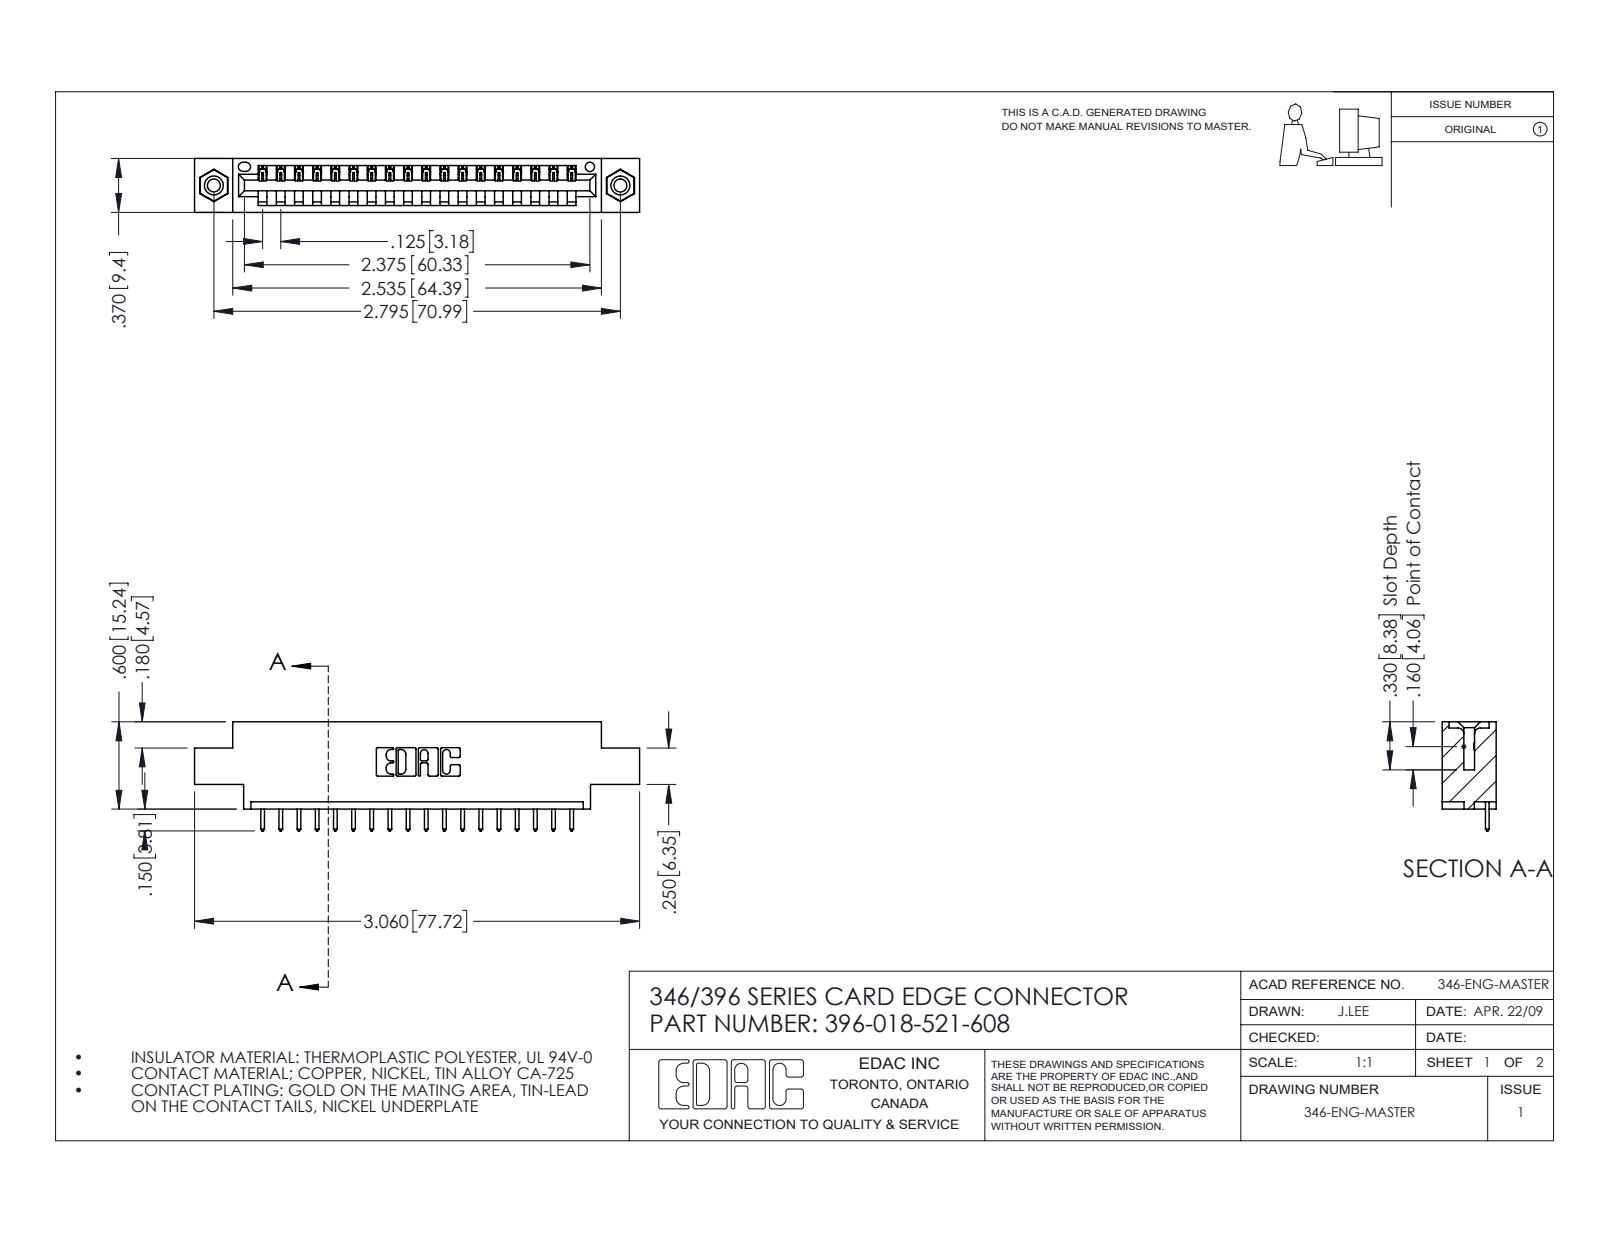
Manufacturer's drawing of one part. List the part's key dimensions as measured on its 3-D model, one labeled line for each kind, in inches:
Part name (STEP PRODUCT): 346 Part_0.170 Offset - 0.156 Dia-TI; 345-292-001_345-293-121; 345-250-001_345-250-003-102; 396-018-521-608
STEP written by: SolidWorks 2016 (CONFIG_CONTROL_DESIGN)
Units: inches
Bodies: 21 solids, 1230 faces (832 planar, 382 cylindrical, 16 other)
Overall size (bounding box): 3.06 × 0.75 × 0.37
Volume: 0.431 in³ · Surface area: 13.25 in²
Round holes (diameter × count): ⌀0.089 ×2, ⌀0.125 ×2, ⌀0.156 ×2, ⌀0.064 ×1
Round bosses / shafts (diameter × count): ⌀0.155 ×2
Partial cylindrical surfaces — rounded edges, fillets, slot ends (radius × count): R0.006 ×36, R0.01 ×36, R0.01 ×22, R0.007 ×6, R0.031 ×6, R0.026 ×3, R0.031 ×2, R0.04 ×2
Main face-to-face distances: 0.048, 0.322, 0.37, 0.25, 0.222, 0.148, 0.072, 0.298, 0.025, 0.1
Hole centre spacings: 0.246, 2.588, 2.795
